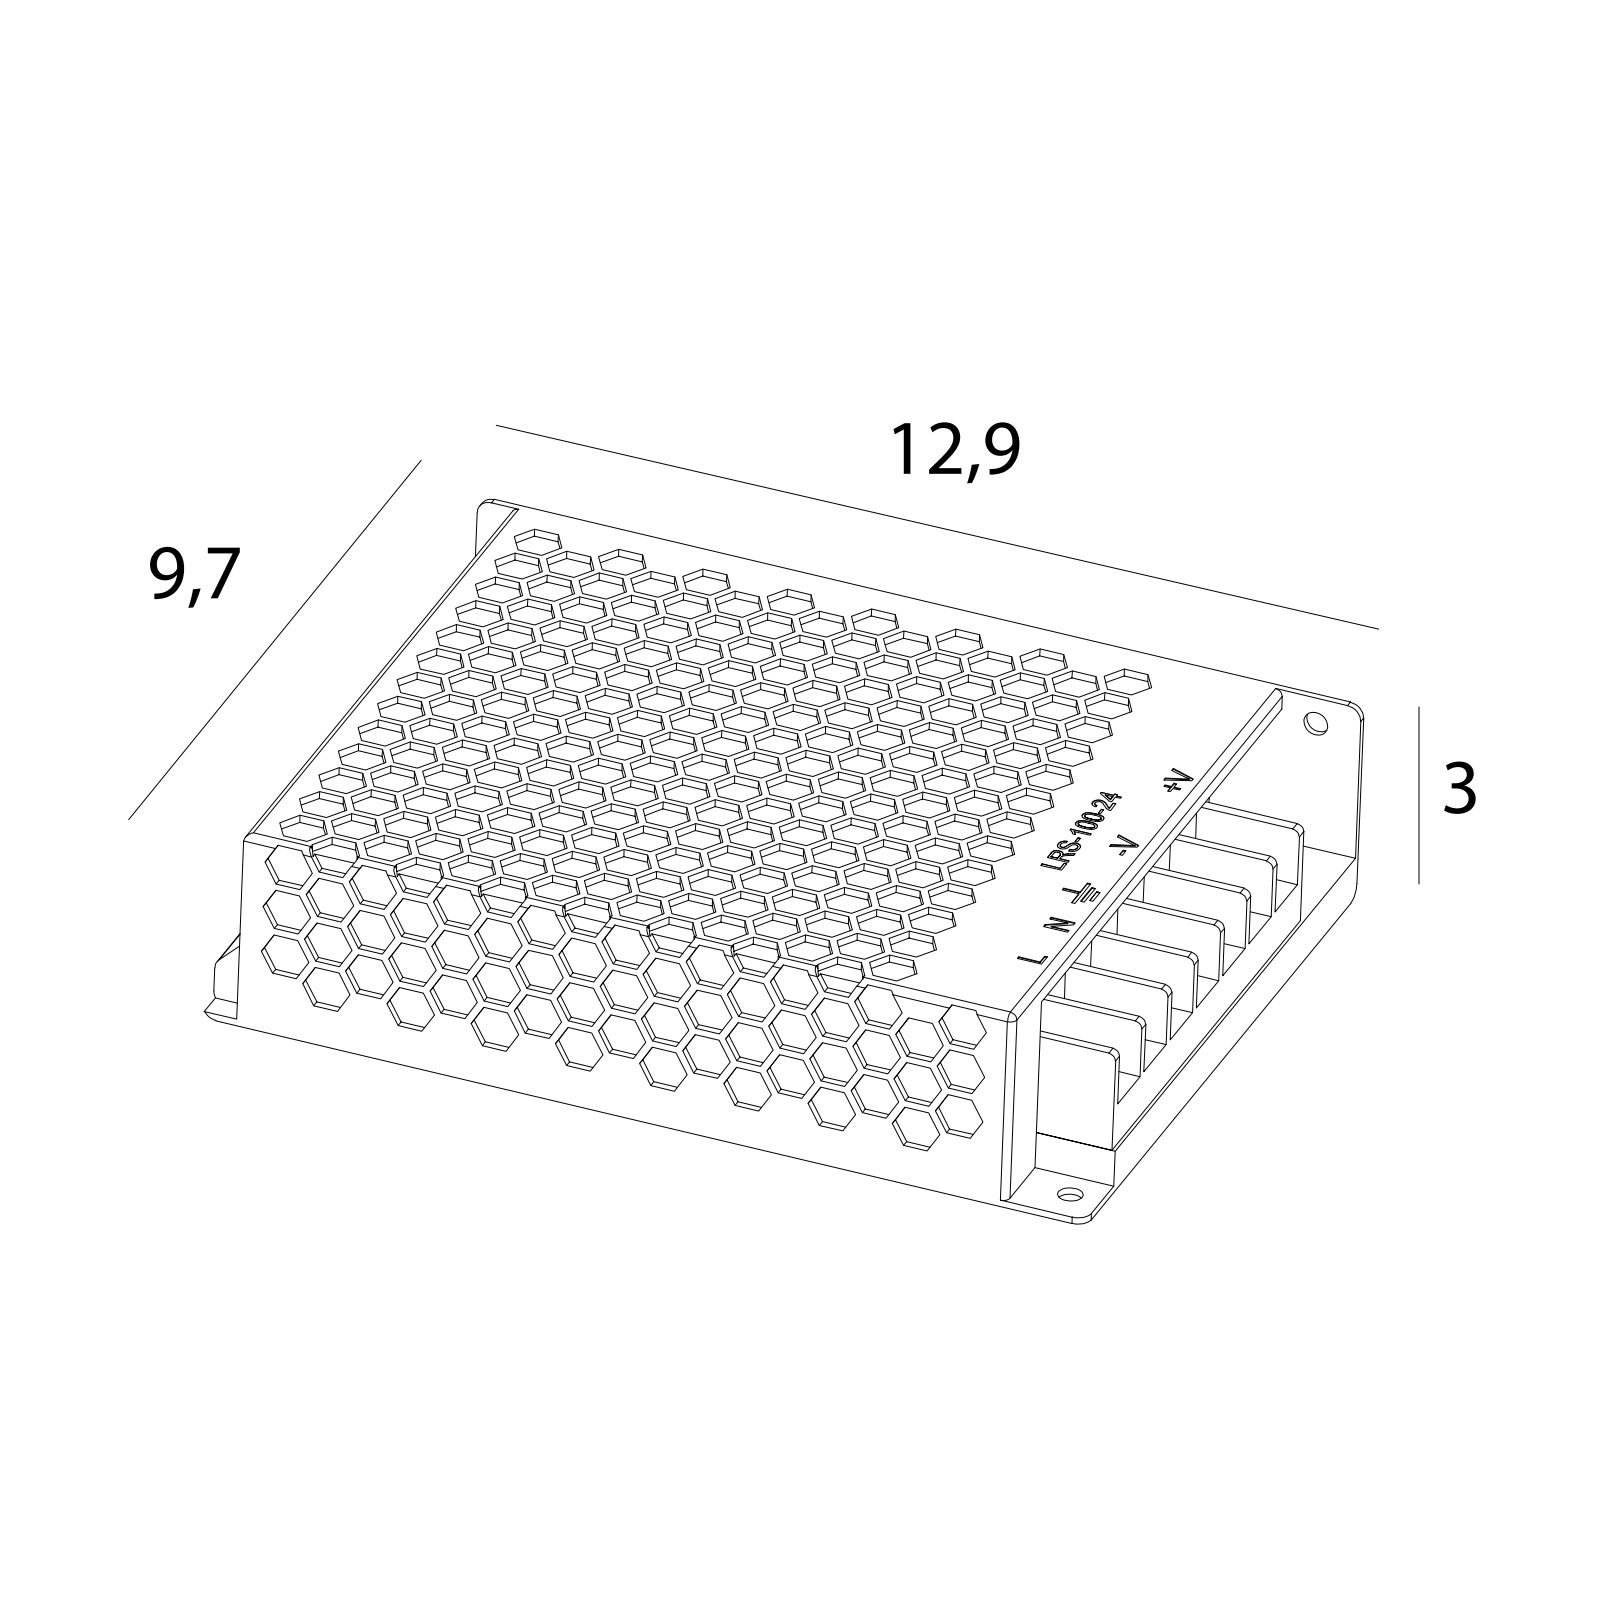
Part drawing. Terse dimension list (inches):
name: NA0008 v1
written by: Autodesk Translation Framework v14.24.0.0 (AUTOMOTIVE_DESIGN)
unit: in
bodies: 1 solid, 2081 faces (1971 planar, 41 cylindrical, 69 other)
size: 5.079 × 3.819 × 1.181
volume: 19.53 in³; area: 78.34 in²
holes: 5× ⌀0.098, 2× ⌀0.138
rounds: 8× R0.039, 7× R0.079, 3× R0.157, 2× R0.069
face distances: 0.043, 1.138, 1.181, 0.118, 4.035, 3.776, 3.819, 0.37, 0.256, 0.74
hole spacings: 3.052, 0.709, 1.093, 1.299, 3.05, 3.674, 4.036, 4.111
